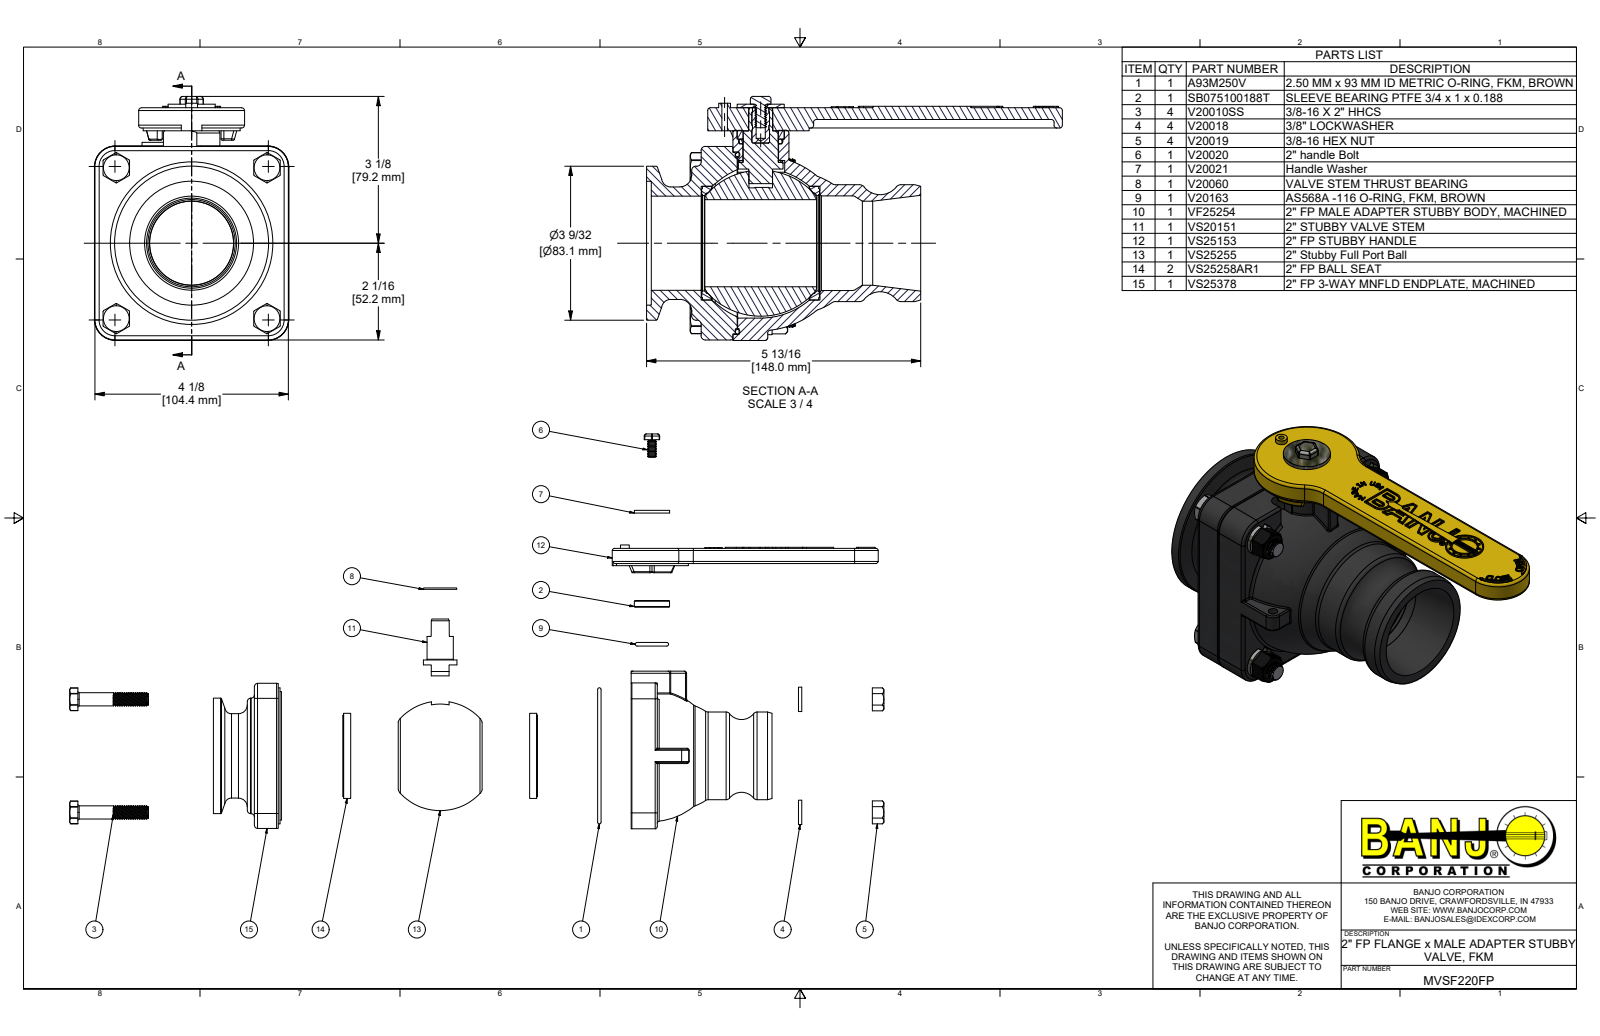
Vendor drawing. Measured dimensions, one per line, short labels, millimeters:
name: MVSF220FP; VF25254; VF25254X; VS20151 (+8 more)
written by: Autodesk Inventor 2022 (AUTOMOTIVE_DESIGN)
unit: mm
bodies: 26 solids, 1885 faces (615 planar, 569 cylindrical, 701 other)
size: 224.4 × 131.6 × 104.9
volume: 618 900 mm³; area: 187 500 mm²
holes: 8× ⌀11.6, 5× ⌀9.5, 4× ⌀7.8, 4× ⌀9.8, 2× ⌀5.1, 1× ⌀2.3, 1× ⌀3, 1× ⌀5, 1× ⌀7.1, 1× ⌀8.9, 1× ⌀13.8, 1× ⌀19.1
bosses: 60× ⌀8.2, 4× ⌀17.4, 4× ⌀9.5, 1× ⌀97.8, 1× ⌀92.3, 1× ⌀92.1, 1× ⌀83.1, 1× ⌀63
rounds: 31× R1.5, 22× R0.8, 8× R2.3, 8× R4.1, 4× R8.1, 4× R10.8, 4× R11.4, 3× R5.1
face distances: 104.6, 17.1, 35.9, 18.8, 6.4, 104.4, 104.9, 29.5, 46.6, 65.4
hole spacings: 81.3, 57.5, 57.5, 81.3, 81.4, 115, 51.8, 62.4
